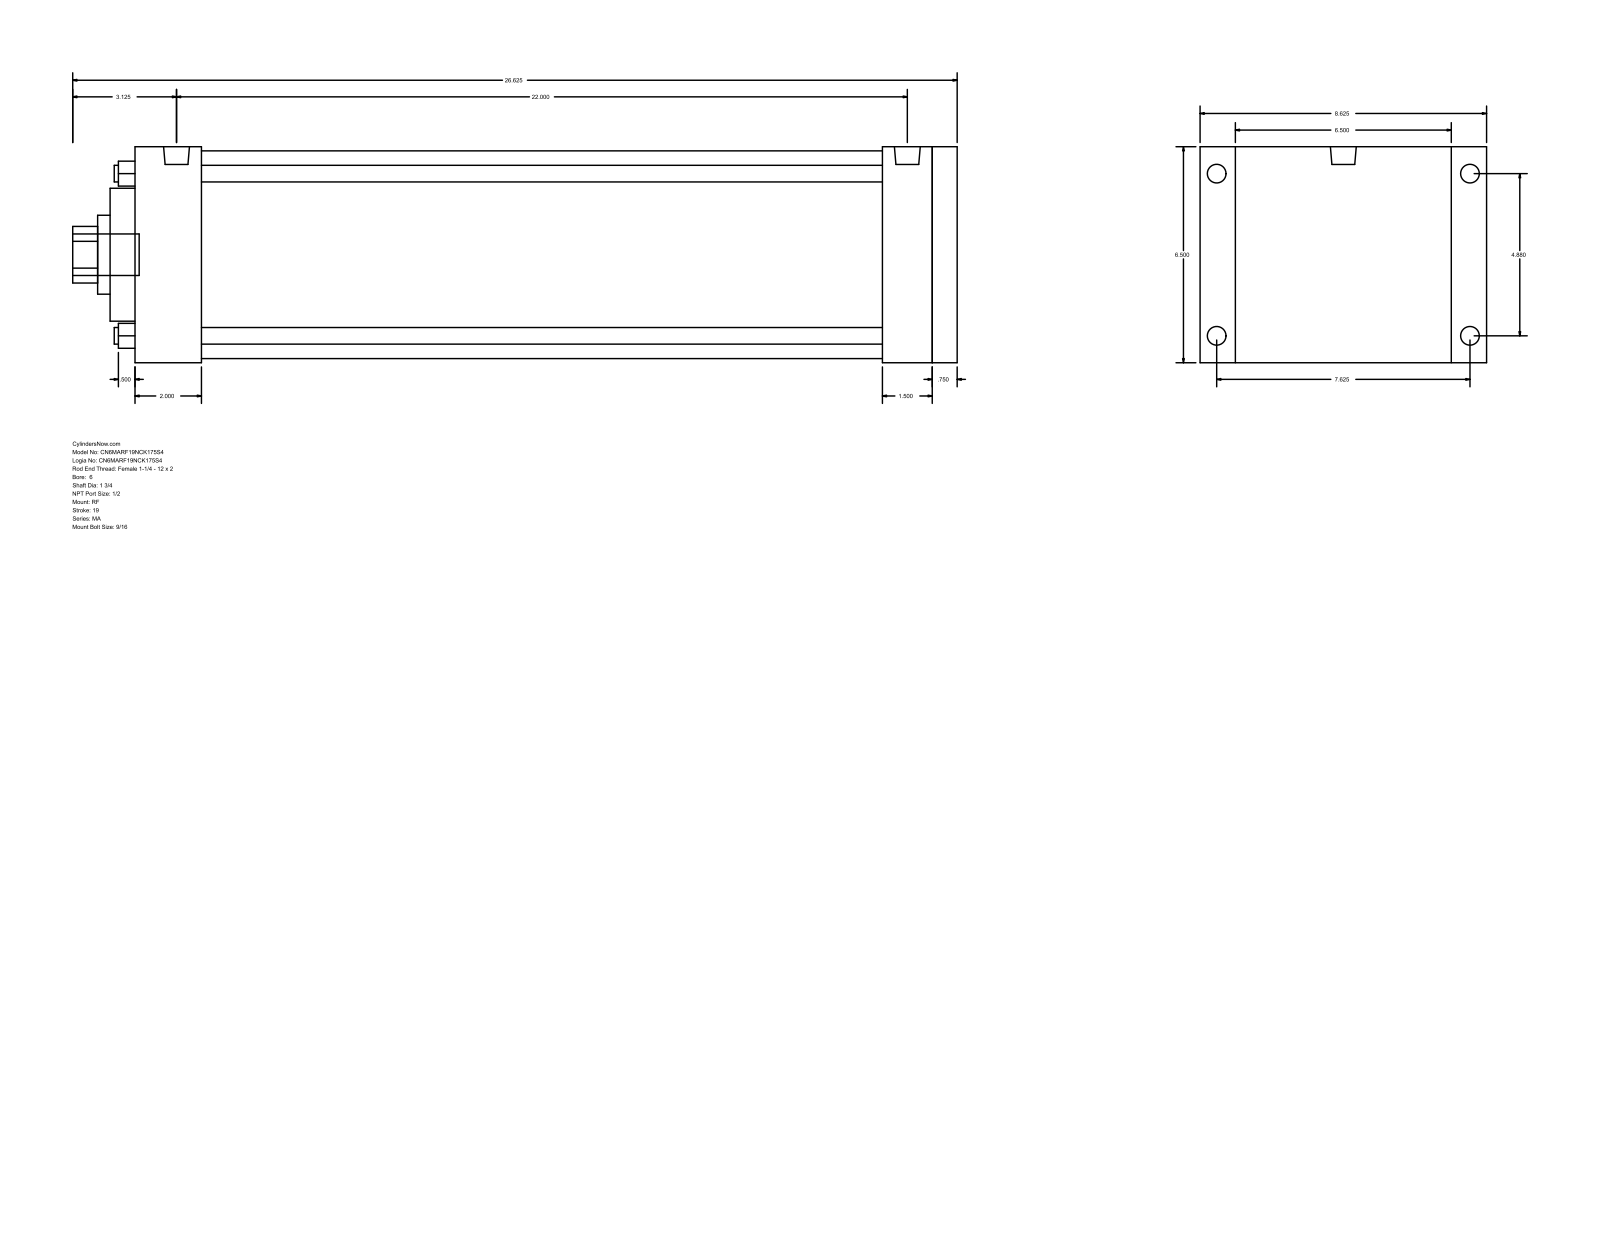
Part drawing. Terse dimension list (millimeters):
name: MA_RF__0600_1.75
written by: GSSL Pune (CONFIG_CONTROL_DESIGN)
unit: mm
bodies: 0 solids, 94 faces (65 planar, 29 cylindrical, 0 other)
size: 676.27 × 219.07 × 165.1
holes: 4× ⌀12.7, 1× ⌀44.45, 1× ⌀60.33, 1× ⌀101.6, 1× ⌀158.75
bosses: 4× ⌀17.46, 4× ⌀14.29, 2× ⌀19.77, 1× ⌀31.75
rounds: 1× R21.63
face distances: 165.1, 628.65, 19.04, 609.61, 19.05, 50.8, 558.81, 577.85, 571.5, 520.7
hole spacings: 87.65, 123.96, 175.31
